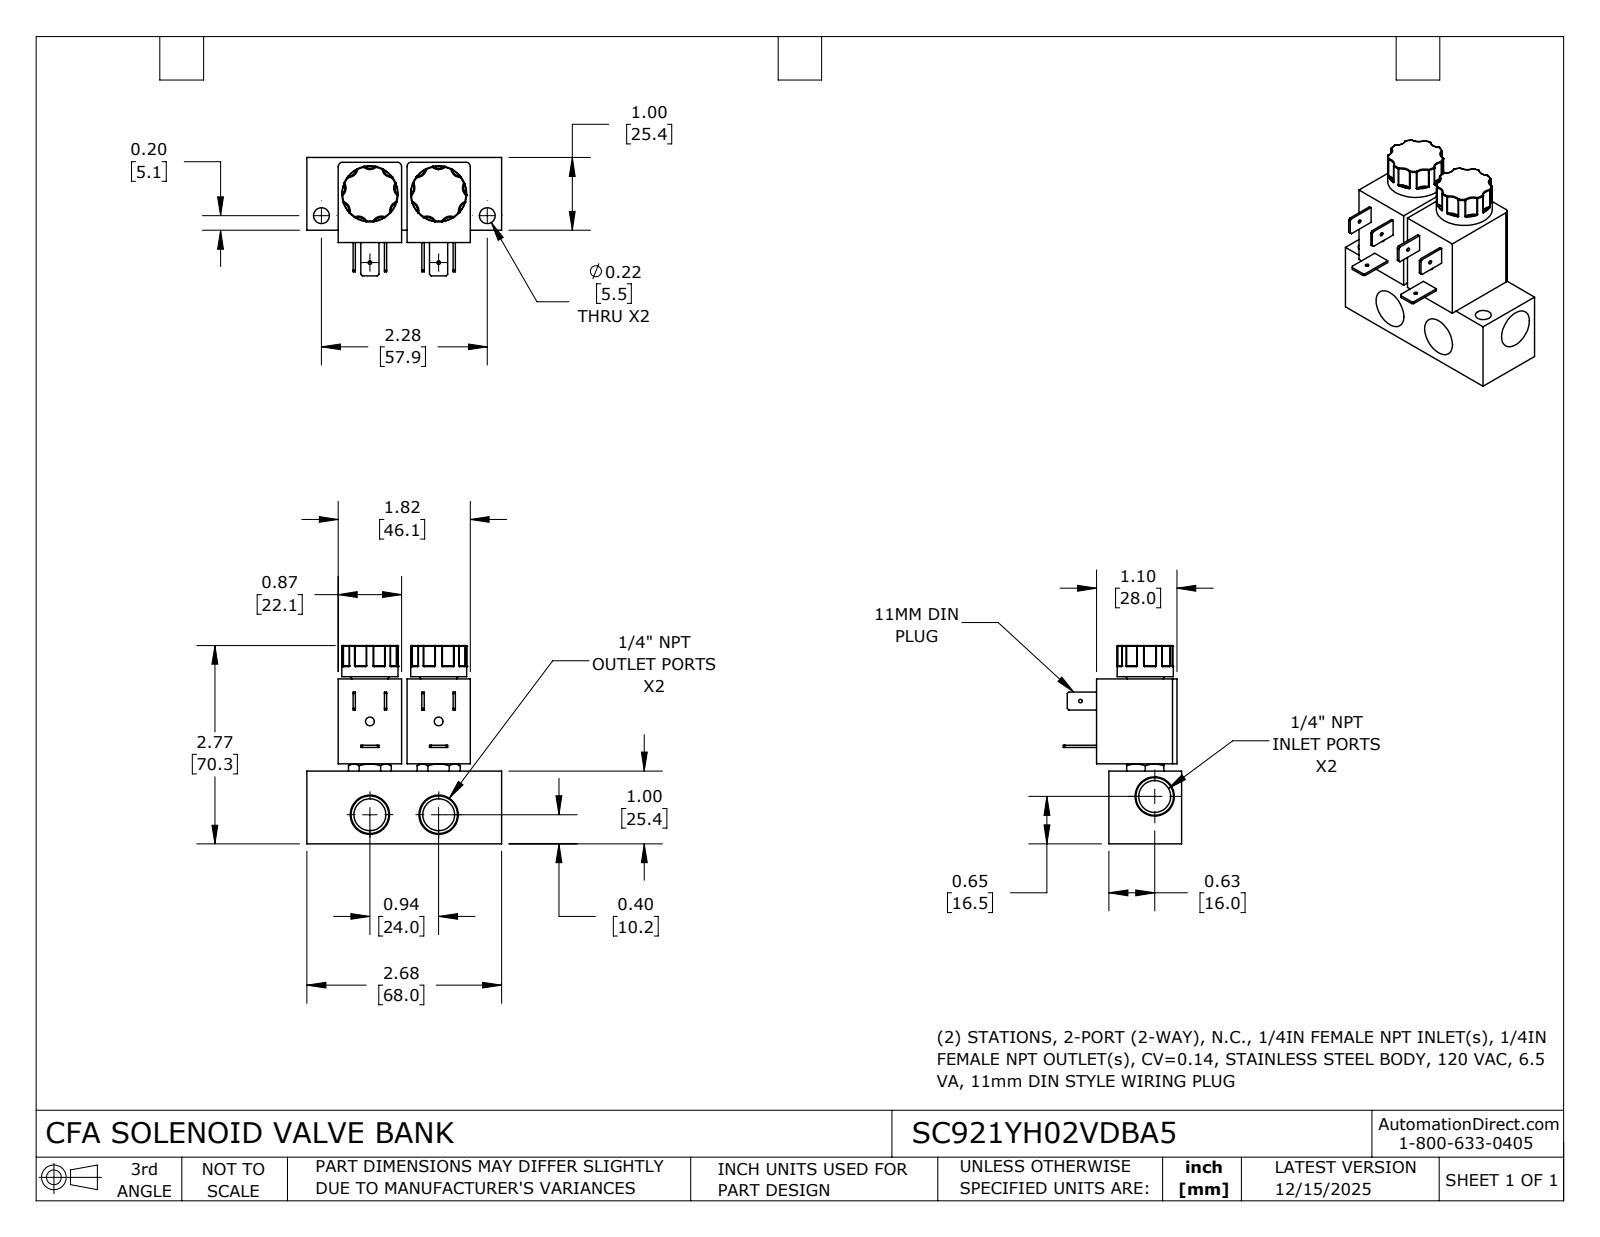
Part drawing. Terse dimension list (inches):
name: SC921YH02VDBA5
written by: SolidWorks 2024 (CONFIG_CONTROL_DESIGN)
unit: in
bodies: 1 solid, 446 faces (100 planar, 96 cylindrical, 250 other)
size: 2.725 × 2.677 × 1.627
volume: 4.833 in³; area: 34.57 in²
holes: 3× ⌀0.05, 3× ⌀0.438, 2× ⌀0.12, 2× ⌀0.217
bosses: 2× ⌀0.77
rounds: 36× R0.01, 18× R0.133, 4× R0.06
face distances: 1, 0.945, 0.87, 1.169, 0.169, 0.065, 0.935, 1.104, 0.431, 1.301
hole spacings: 0.945, 1.282, 1.593, 0.928, 0.93, 1.662, 1.735, 1.738
